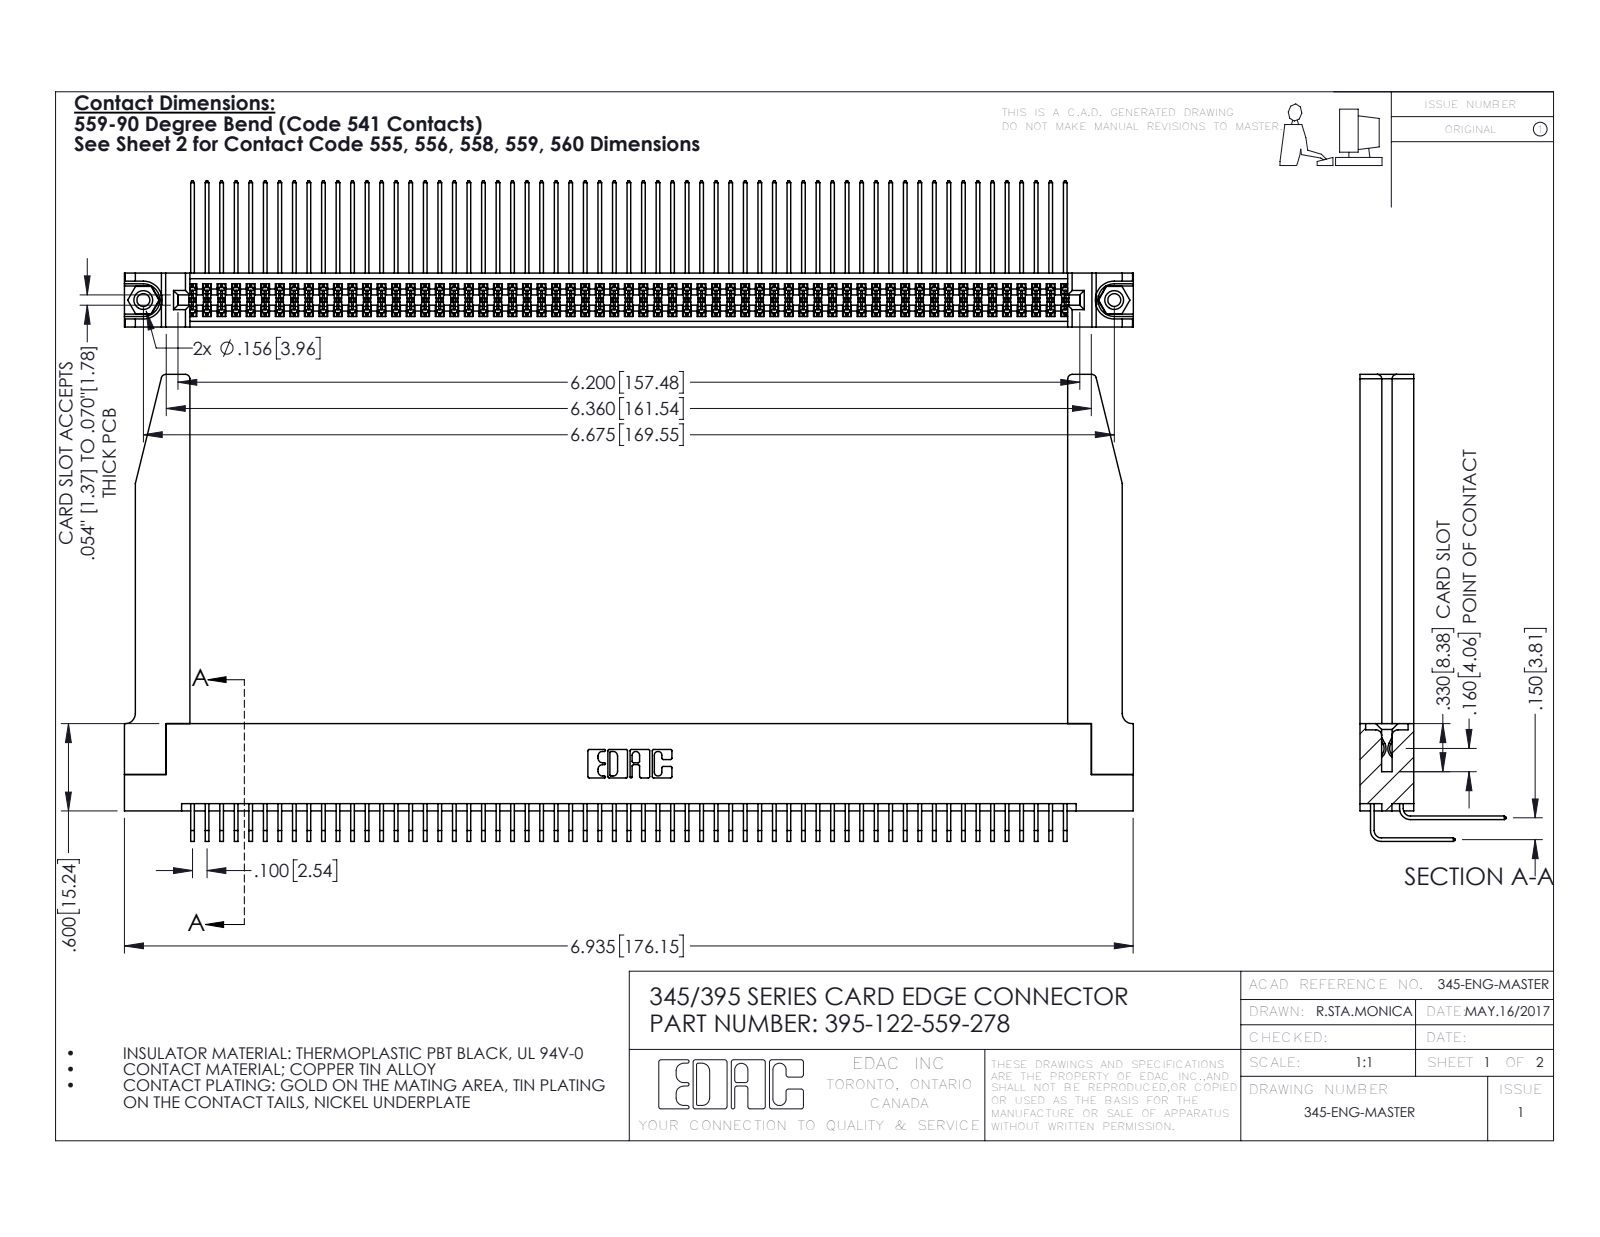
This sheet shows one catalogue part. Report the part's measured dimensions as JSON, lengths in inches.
{"part_name": "345 Part_Flush Mounting Lugs - 0.156 Dia-TH; 345-292-001_558 559 Tail - 1; 345-220-078_345-220-078; 345-292-001_559 Tail - 2 (+2 more)", "step_written_by": "SolidWorks 2016 (CONFIG_CONTROL_DESIGN)", "units": "inches", "bodies": {"solids": 127, "faces": 6704, "planar": 4492, "cylindrical": 2160, "other": 52}, "overall_size": [6.936, 3.209, 1.005], "volume_in3": 1.572, "surface_area_in2": 57.53, "round_holes": [[0.089, 2], [0.125, 2], [0.156, 2], [0.064, 1]], "round_bosses_or_shafts": [[0.155, 2]], "partial_cylinders_radius": [[0.006, 183], [0.01, 22], [0.03, 8], [0.007, 6], [0.031, 6], [0.026, 3], [0.014, 2], [0.019, 2]], "face_to_face_distances": [0.072, 0.298, 0.37, 0.2, 0.098, 0.272, 0.025, 0.225, 0.175, 0.15], "hole_center_spacings": [0.27, 6.439, 6.675]}
